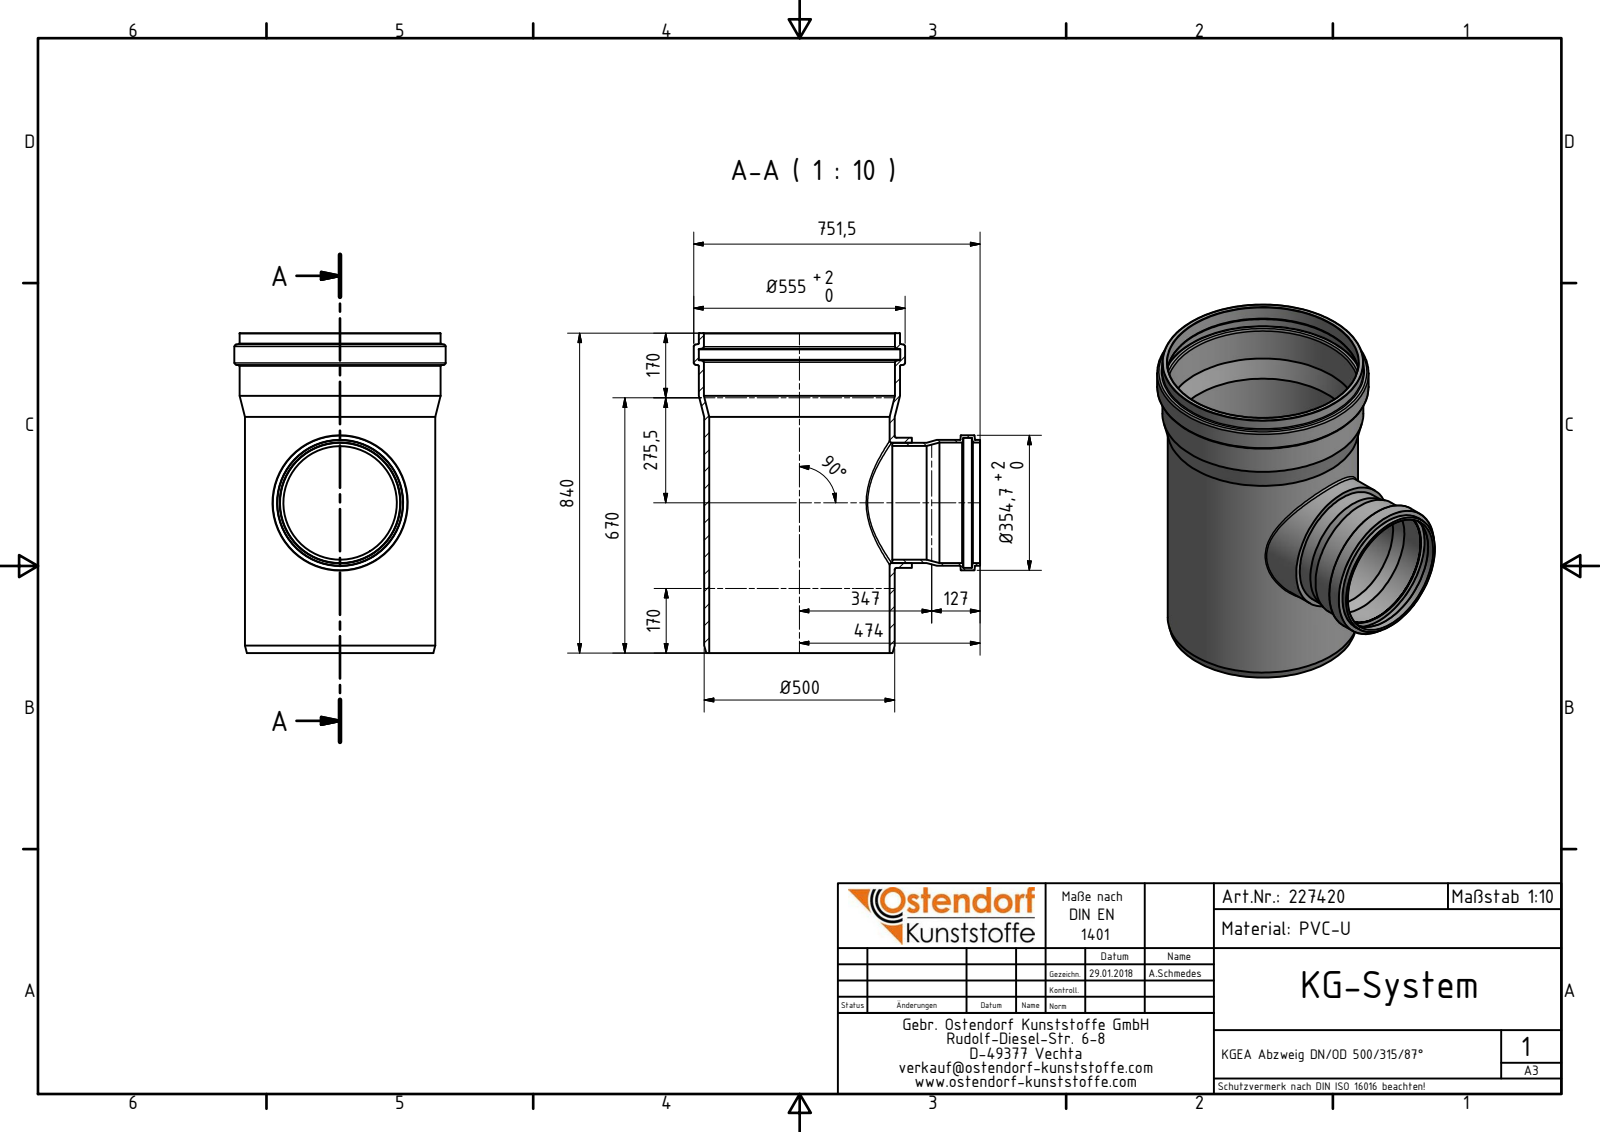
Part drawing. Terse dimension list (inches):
name: 227420 KGEA Abzweig DN_OD 500_315_87°; 227420 KGEA Abzweig DN_OD 500_315_87° Abzweig
written by: Autodesk Inventor 2016 (AUTOMOTIVE_DESIGN)
unit: in
bodies: 2 solids, 60 faces (6 planar, 19 cylindrical, 35 other)
size: 33.071 × 29.587 × 21.85
volume: 1 177 in³; area: 5 013 in²
holes: 1× ⌀11.74, 1× ⌀12.425, 1× ⌀12.441, 1× ⌀12.453, 1× ⌀13.421, 1× ⌀18.661, 1× ⌀19.764, 1× ⌀20.827
bosses: 1× ⌀21.85, 1× ⌀20.787, 1× ⌀19.685, 1× ⌀13.965, 1× ⌀13.449, 1× ⌀12.996, 1× ⌀12.984
face distances: 33.071, 2.008, 7.047, 9.055, 1.833, 5.215, 7.222
